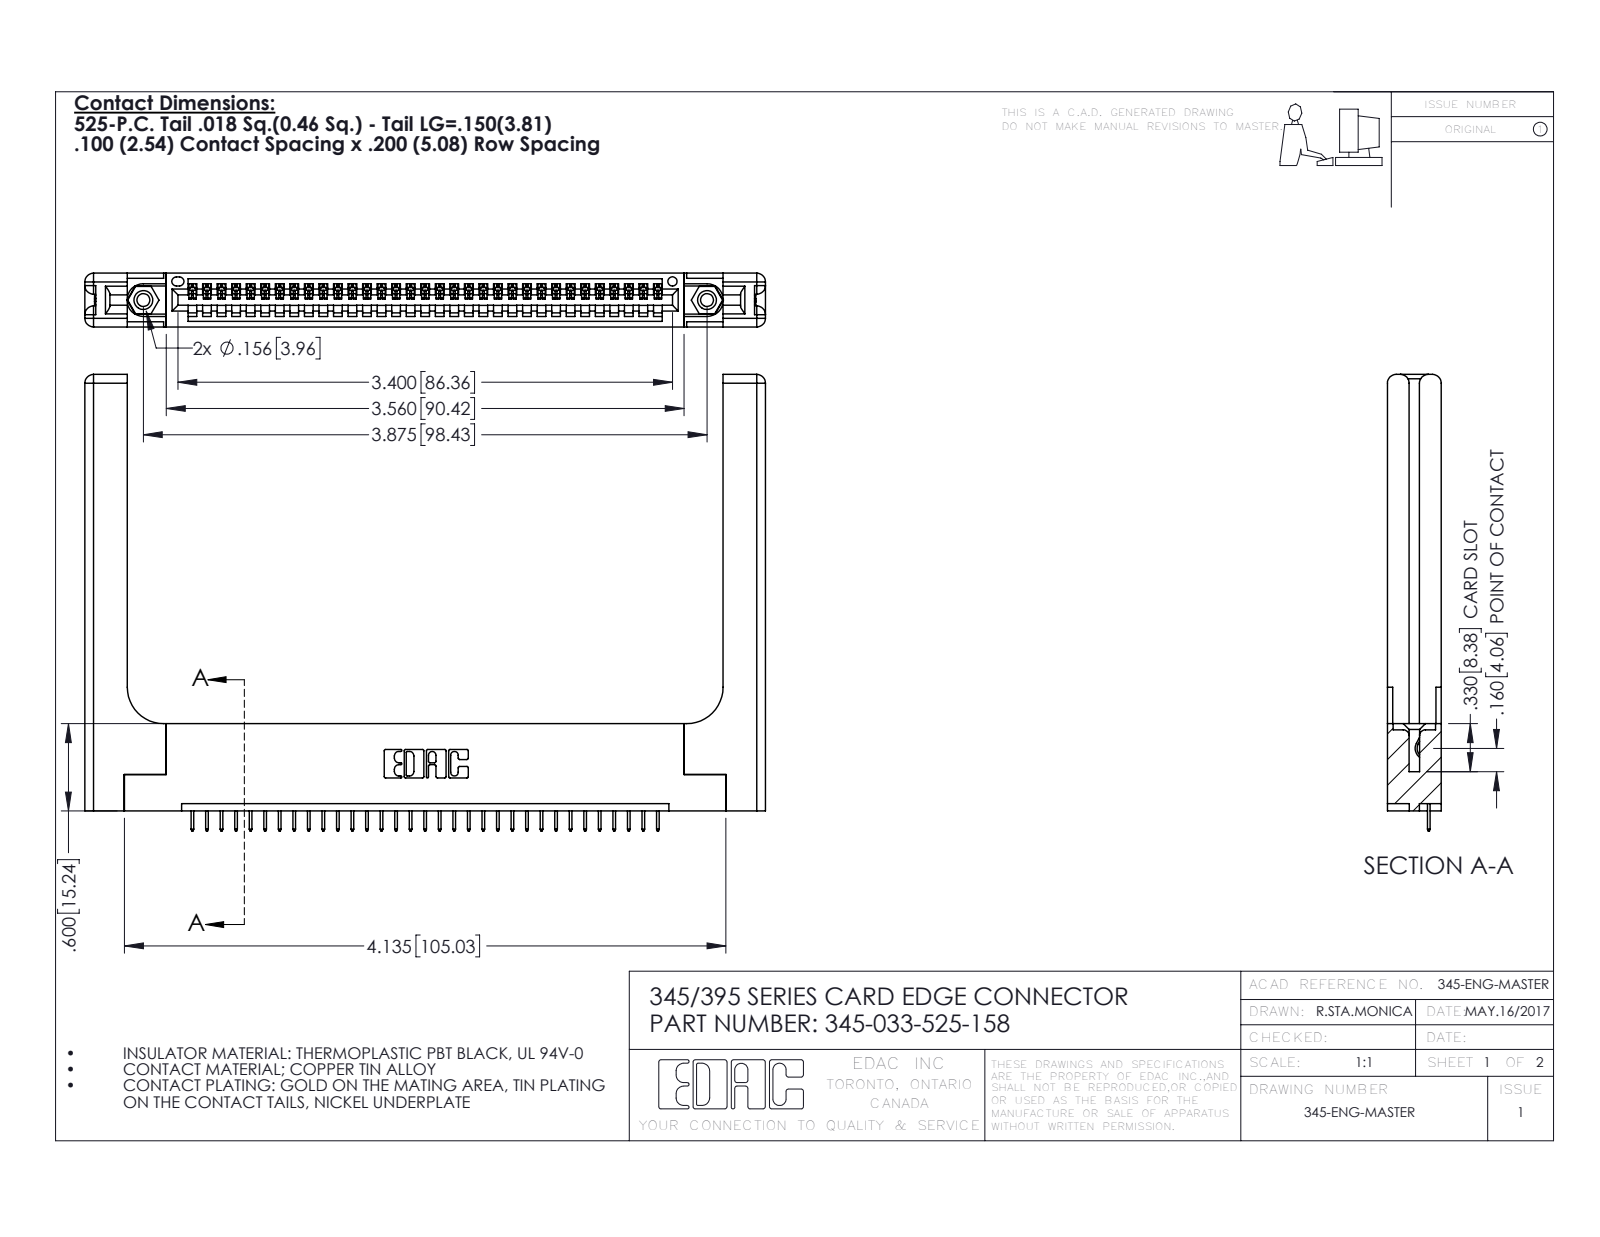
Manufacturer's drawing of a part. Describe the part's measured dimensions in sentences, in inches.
The part is named "345-220-058_345-220-058; 345-033-525-158; 345-250-001_345-250-001-102; 345-292-001_345-293-125 (+1 more)". Its 3-D file was written by "SolidWorks 2020 (CONFIG_CONTROL_DESIGN)". It is 38 solids with 2428 faces: 1746 planar, 622 cylindrical and 60 other. Overall it measures 4.679 by 3.137 by 0.37 inches. Its volume is 1.195 cubic inches and its surface area 30.16 square inches. Round holes: 2 of diameter 0.089, 2 of diameter 0.125, 2 of diameter 0.156, 1 of diameter 0.064. Round bosses or shafts: 2 of diameter 0.155. Partial cylindrical surfaces (rounded edges, fillets, slot ends): 66 of radius 0.006, 22 of radius 0.01, 16 of radius 0.06, 6 of radius 0.007, 6 of radius 0.031, 3 of radius 0.026, 2 of radius 0.03, 2 of radius 0.031. The main face-to-face distances are 0.37, 0.072, 0.298, 0.2, 0.148, 0.15, 0.098, 0.272, 0.025, 0.077. The hole center spacings are 0.27, 3.64, 3.875.
